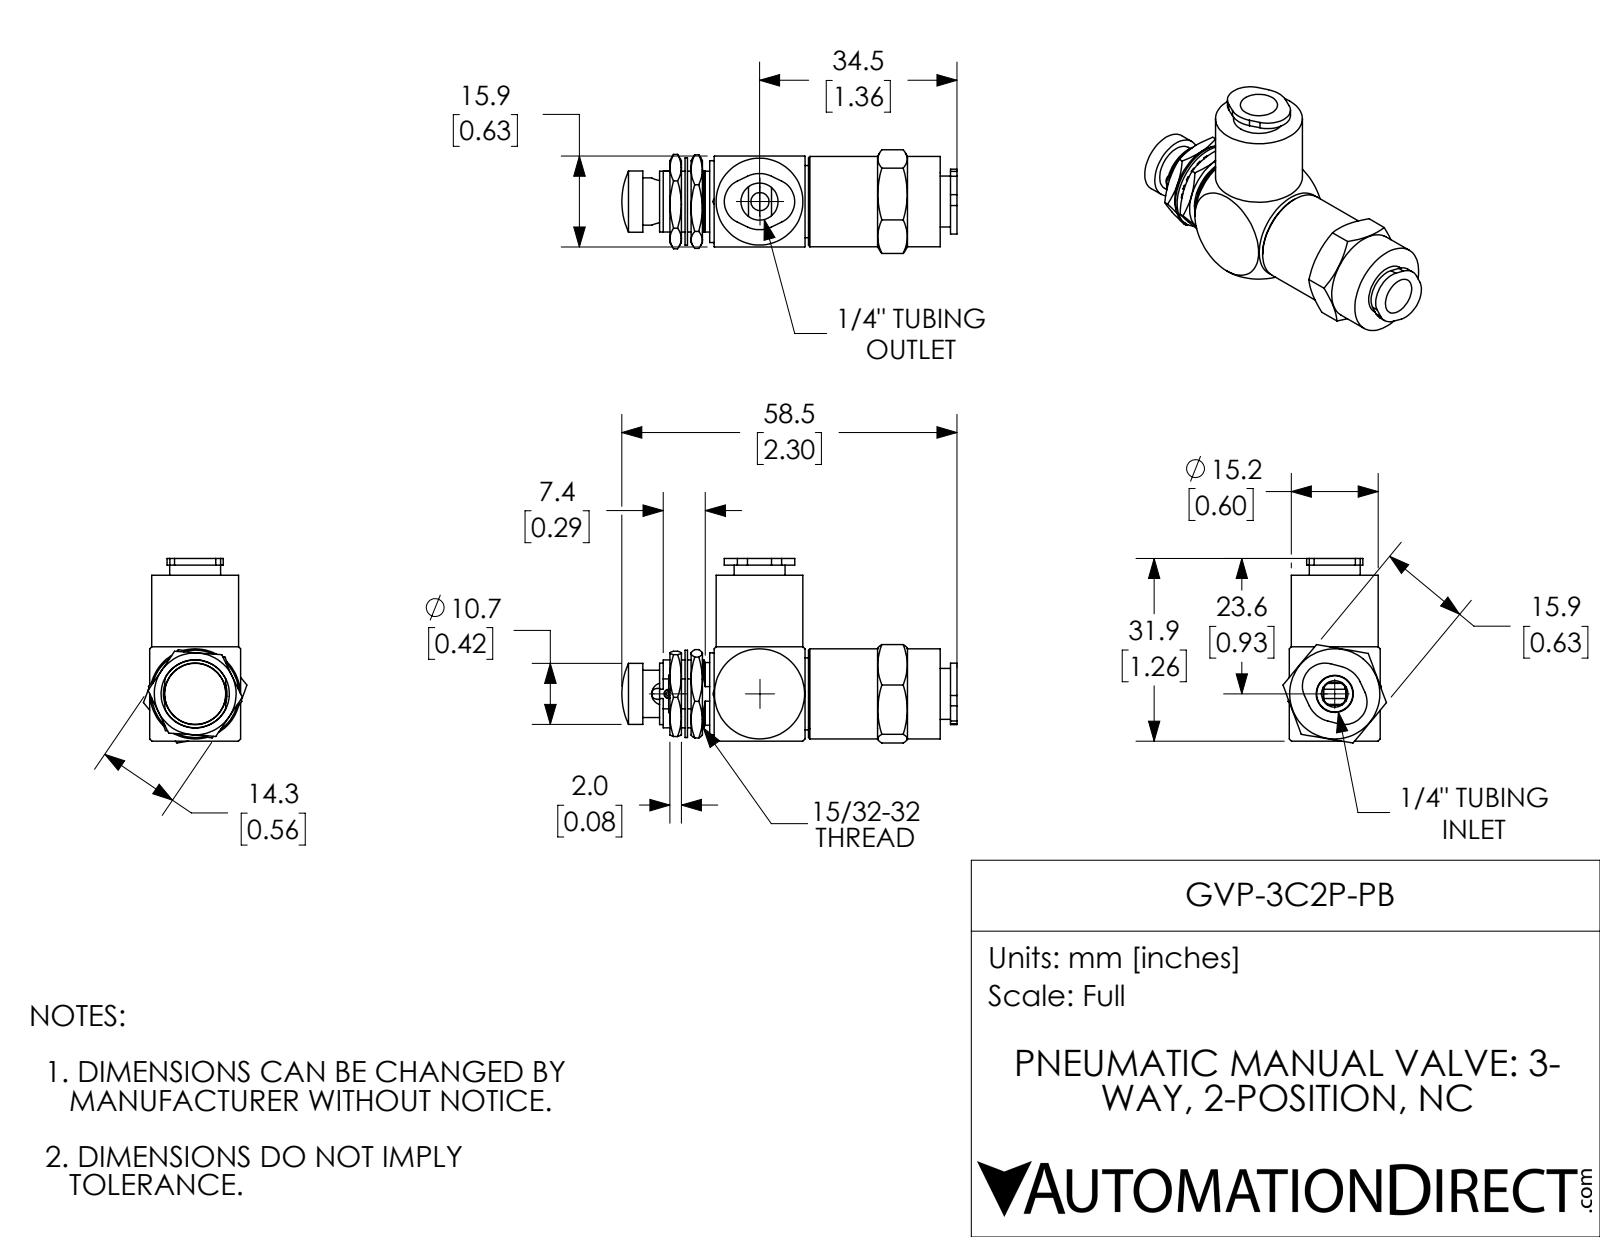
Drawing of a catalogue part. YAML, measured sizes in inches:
part_name: "GVP-3C2P-PB"
step_written_by: "SolidWorks 2018 (AUTOMOTIVE_DESIGN)"
units: inches
bodies: {solids: 8, faces: 351, planar: 134, cylindrical: 156, other: 61}
overall_size: [2.304, 1.268, 0.711]
volume: 0.599
surface_area: 14.26
round_holes:
  - {diameter: 0.063, count: 3}
  - {diameter: 0.125, count: 2}
  - {diameter: 0.255, count: 2}
  - {diameter: 0.03, count: 1}
  - {diameter: 0.153, count: 1}
  - {diameter: 0.182, count: 1}
  - {diameter: 0.249, count: 1}
  - {diameter: 0.34, count: 1}
  - {diameter: 0.377, count: 1}
  - {diameter: 0.438, count: 1}
  - {diameter: 0.468, count: 1}
  - {diameter: 0.5, count: 1}
round_bosses_or_shafts:
  - {diameter: 0.35, count: 2}
  - {diameter: 0.62, count: 1}
  - {diameter: 0.6, count: 1}
  - {diameter: 0.597, count: 1}
  - {diameter: 0.563, count: 1}
  - {diameter: 0.495, count: 1}
  - {diameter: 0.445, count: 1}
  - {diameter: 0.43, count: 1}
partial_cylinders:
  - {radius: 0.156, count: 4}
  - {radius: 0.037, count: 2}
  - {radius: 0.193, count: 2}
  - {radius: 0.233, count: 1}
  - {radius: 0.239, count: 1}
  - {radius: 0.26, count: 1}
face_to_face_distances: [0.625, 0.072, 1.14, 0.115, 0.626, 0.332, 0.128, 0.267, 0.025, 0.042]
hole_center_spacings: [0.291, 0.039, 0.288, 0.338, 0.377, 0.629, 0.669]
